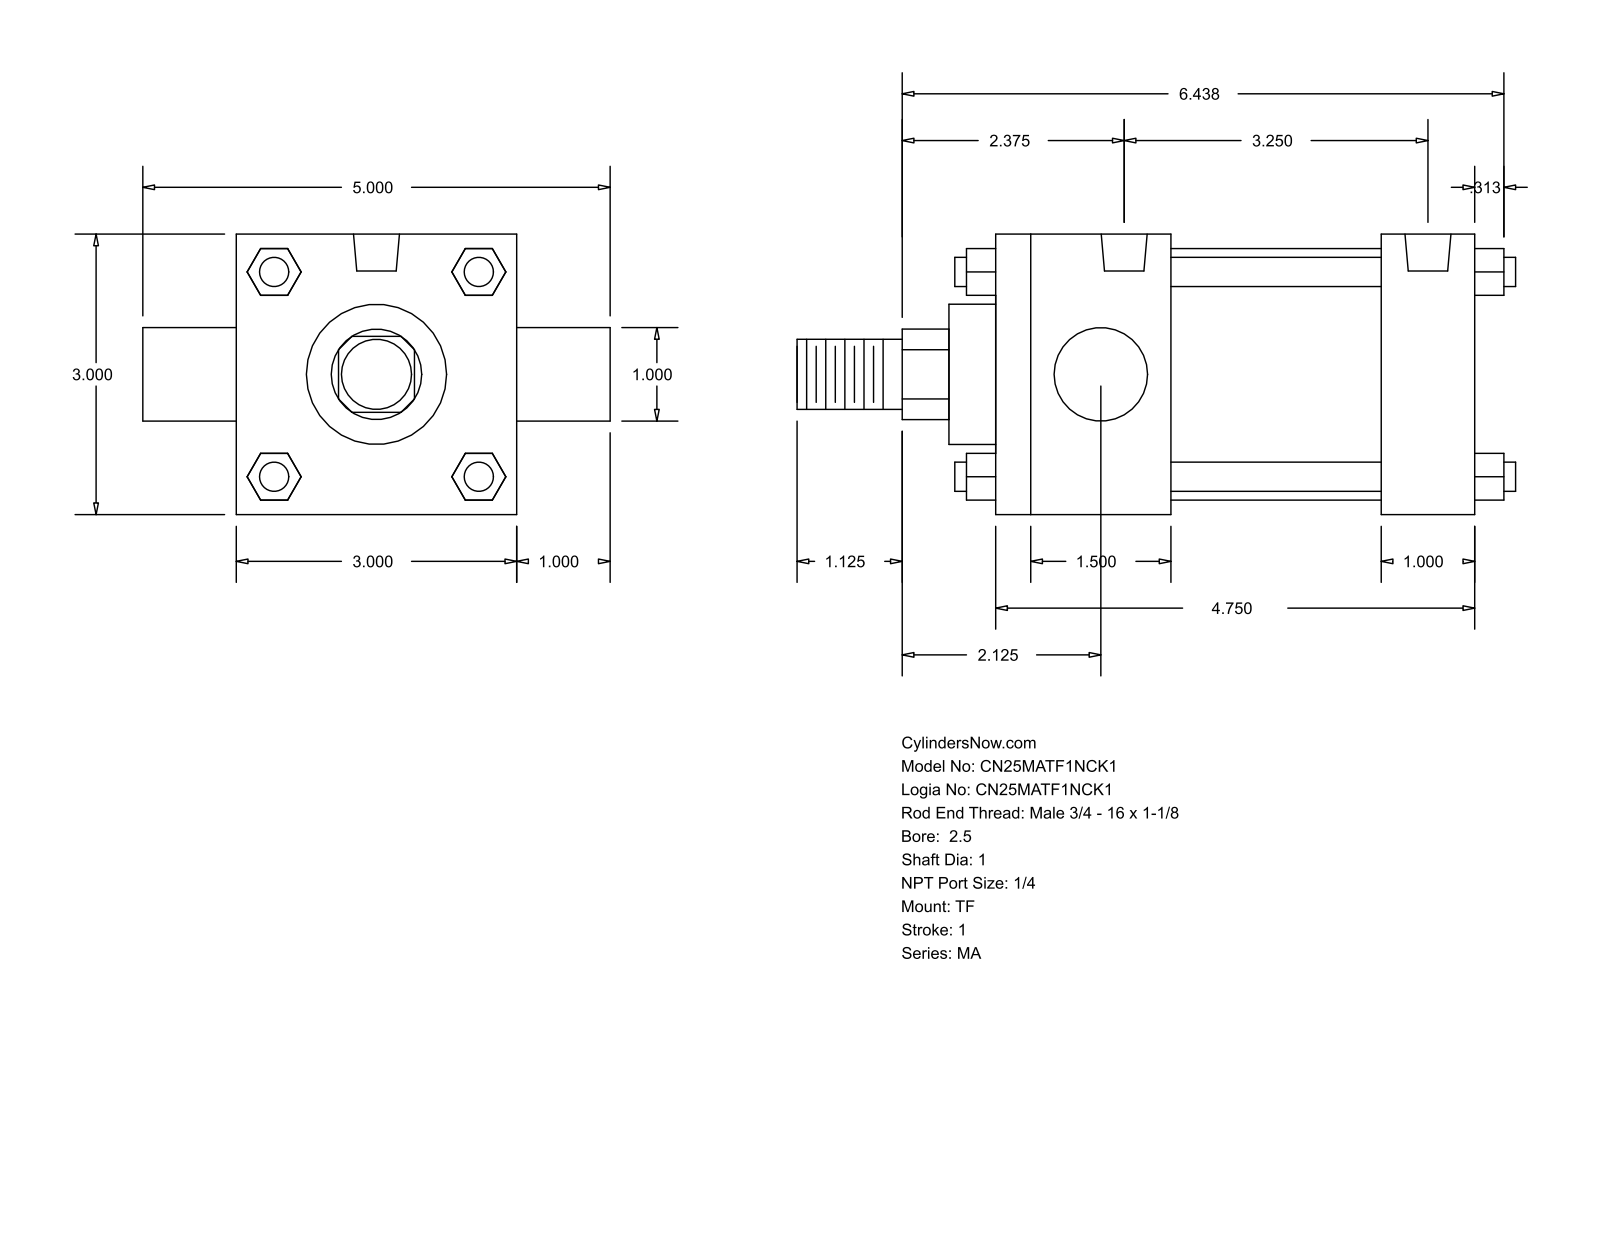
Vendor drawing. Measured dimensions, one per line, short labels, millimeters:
name: MA_TF__0250_1
written by: GSSL Pune (CONFIG_CONTROL_DESIGN)
unit: mm
bodies: 0 solids, 120 faces (92 planar, 28 cylindrical, 0 other)
size: 195.26 × 127 × 76.2
holes: 3× ⌀7.94, 2× ⌀12.49
bosses: 4× ⌀7.94, 2× ⌀25.4, 1× ⌀68.33, 1× ⌀38.1, 1× ⌀19.05
rounds: 1× R12.29
face distances: 76.2, 130.17, 12.7, 47.63, 104.78, 57.15, 82.54, 25.39, 101.6, 25.4
hole spacings: 82.55
